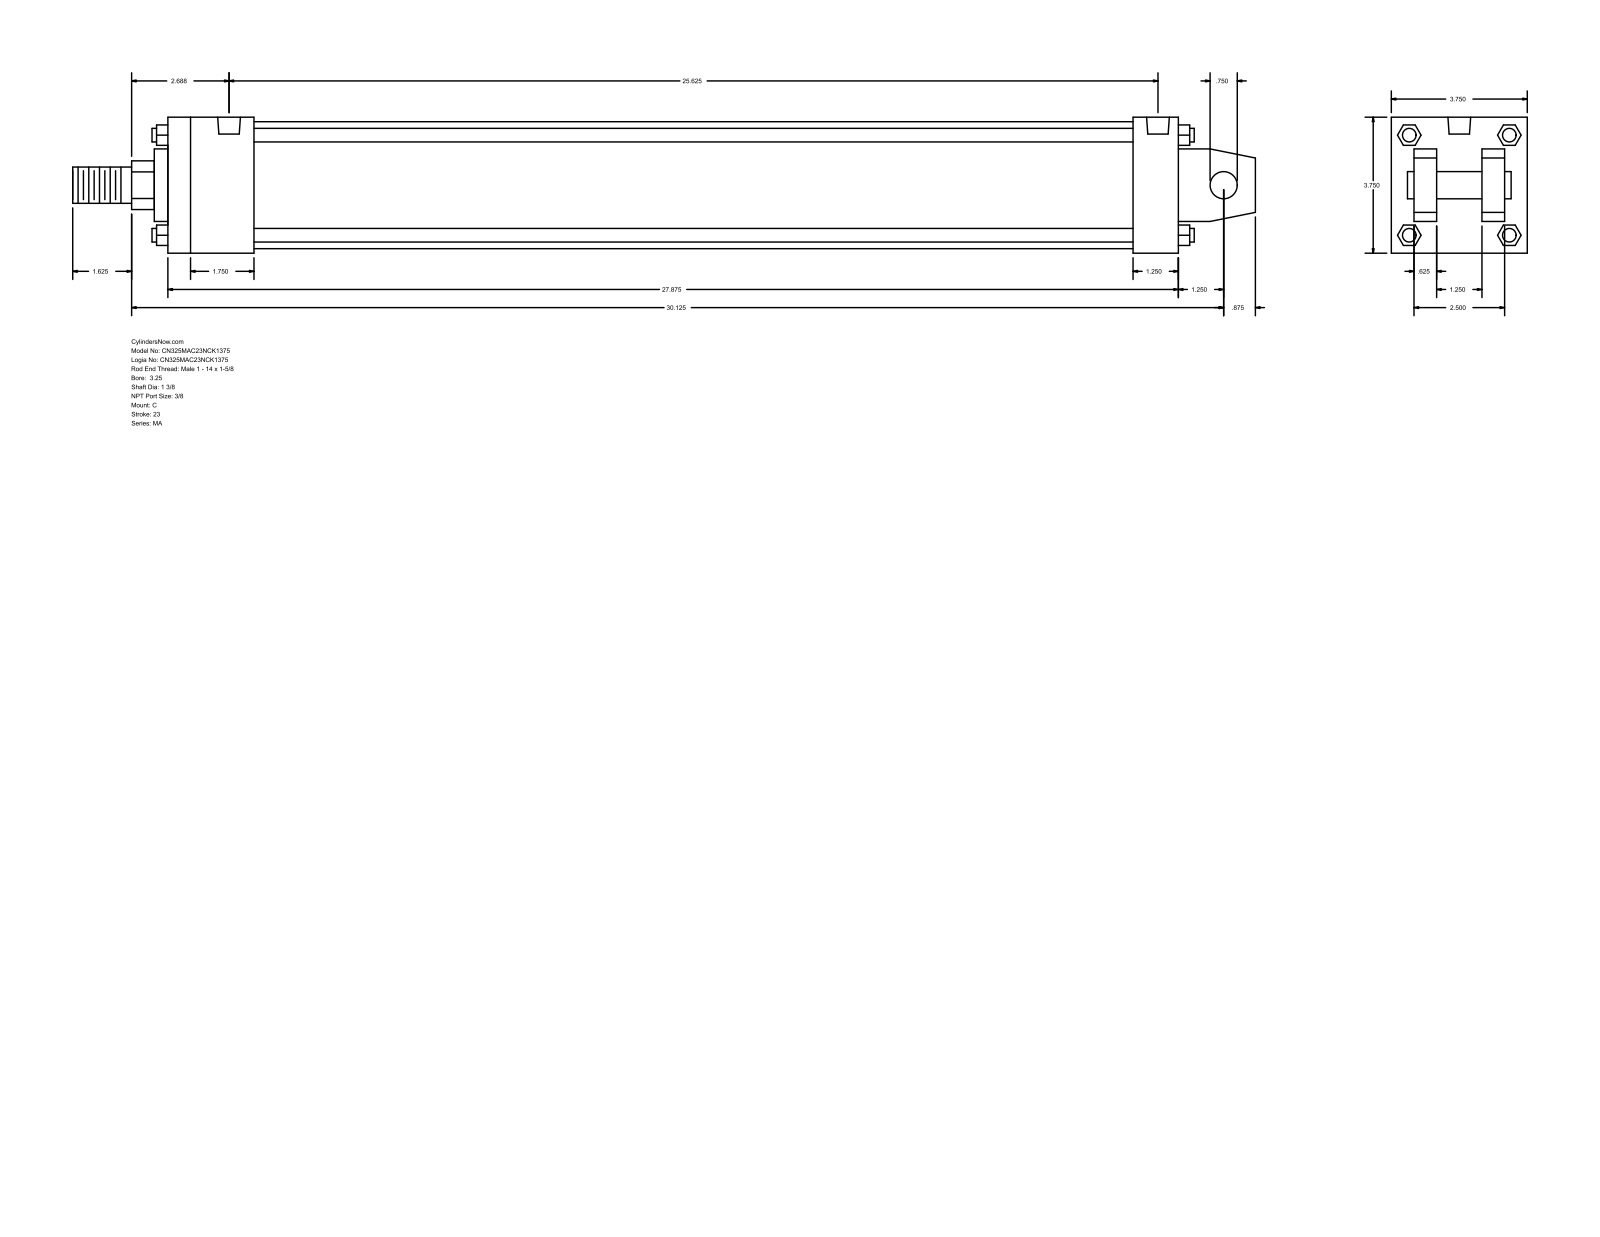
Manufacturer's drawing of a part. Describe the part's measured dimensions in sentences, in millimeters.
The part is named "MA_C__0325_1.375". Its 3-D file was written by "GSSL Pune (CONFIG_CONTROL_DESIGN)". It is 0 solids with 139 faces: 108 planar, 31 cylindrical and 0 other. Overall it measures 828.67 by 95.25 by 95.25 millimeters. Round holes: 4 of diameter 11.11, 2 of diameter 15.93. Round bosses or shafts: 4 of diameter 9.53, 1 of diameter 88.9, 1 of diameter 50.8, 1 of diameter 34.92, 1 of diameter 25.4, 1 of diameter 19.05. Partial cylindrical surfaces (rounded edges, fillets, slot ends): 1 of radius 17.06. The main face-to-face distances are 95.24, 15.87, 63.5, 708.02, 31.74, 79.37, 47.63, 676.27, 31.75, 60.32. The hole center spacings are 641.35, 4.76, 4.77, 646.11, 646.12, 650.88.
